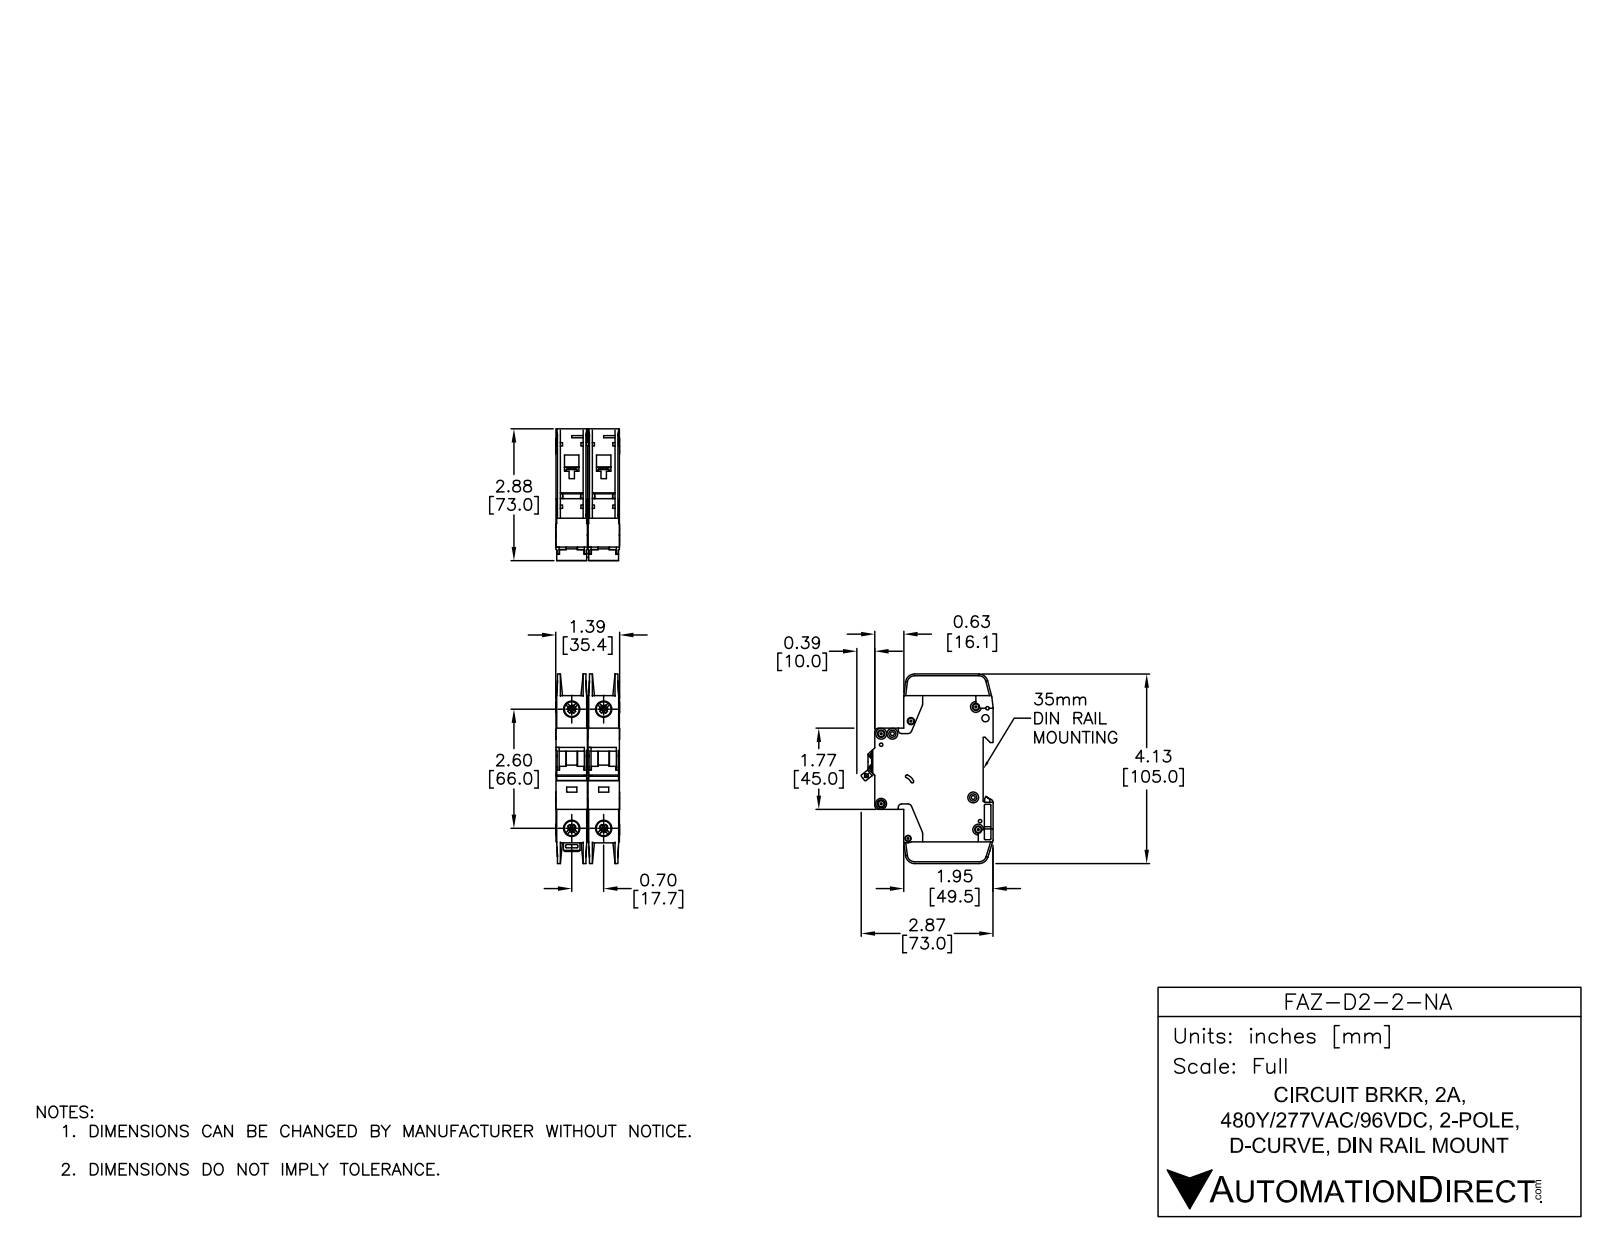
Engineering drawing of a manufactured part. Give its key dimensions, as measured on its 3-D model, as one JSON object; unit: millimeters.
{"part_name": "FAZ-D2-2-NA", "step_written_by": "SolidWorks 2014 (AUTOMOTIVE_DESIGN)", "units": "millimeters", "bodies": {"solids": 6, "faces": 1568, "planar": 818, "cylindrical": 526, "other": 224}, "overall_size": [105, 73.04, 35.4], "volume_mm3": 155390, "surface_area_mm2": 49479, "round_holes": [[3.6, 7], [7.15, 4], [8.2, 4], [1.09, 2], [1.5, 2], [4, 2], [1.9, 1], [2.15, 1], [2.2, 1], [2.55, 1], [3.3, 1], [3.4, 1]], "round_bosses_or_shafts": [[6, 7], [2.5, 2]], "partial_cylinders_radius": [[0.25, 47], [0.5, 24], [1, 18], [2, 12], [5, 5], [1.8, 4], [4, 4], [0.2, 2]], "face_to_face_distances": [17.7, 17.5, 0.7, 15.05, 2.45, 1.75, 15.75, 13.3, 35.2, 17], "hole_center_spacings": [6.2, 17.7, 66, 68.33, 5.19, 6.1, 8.19, 8.56]}
